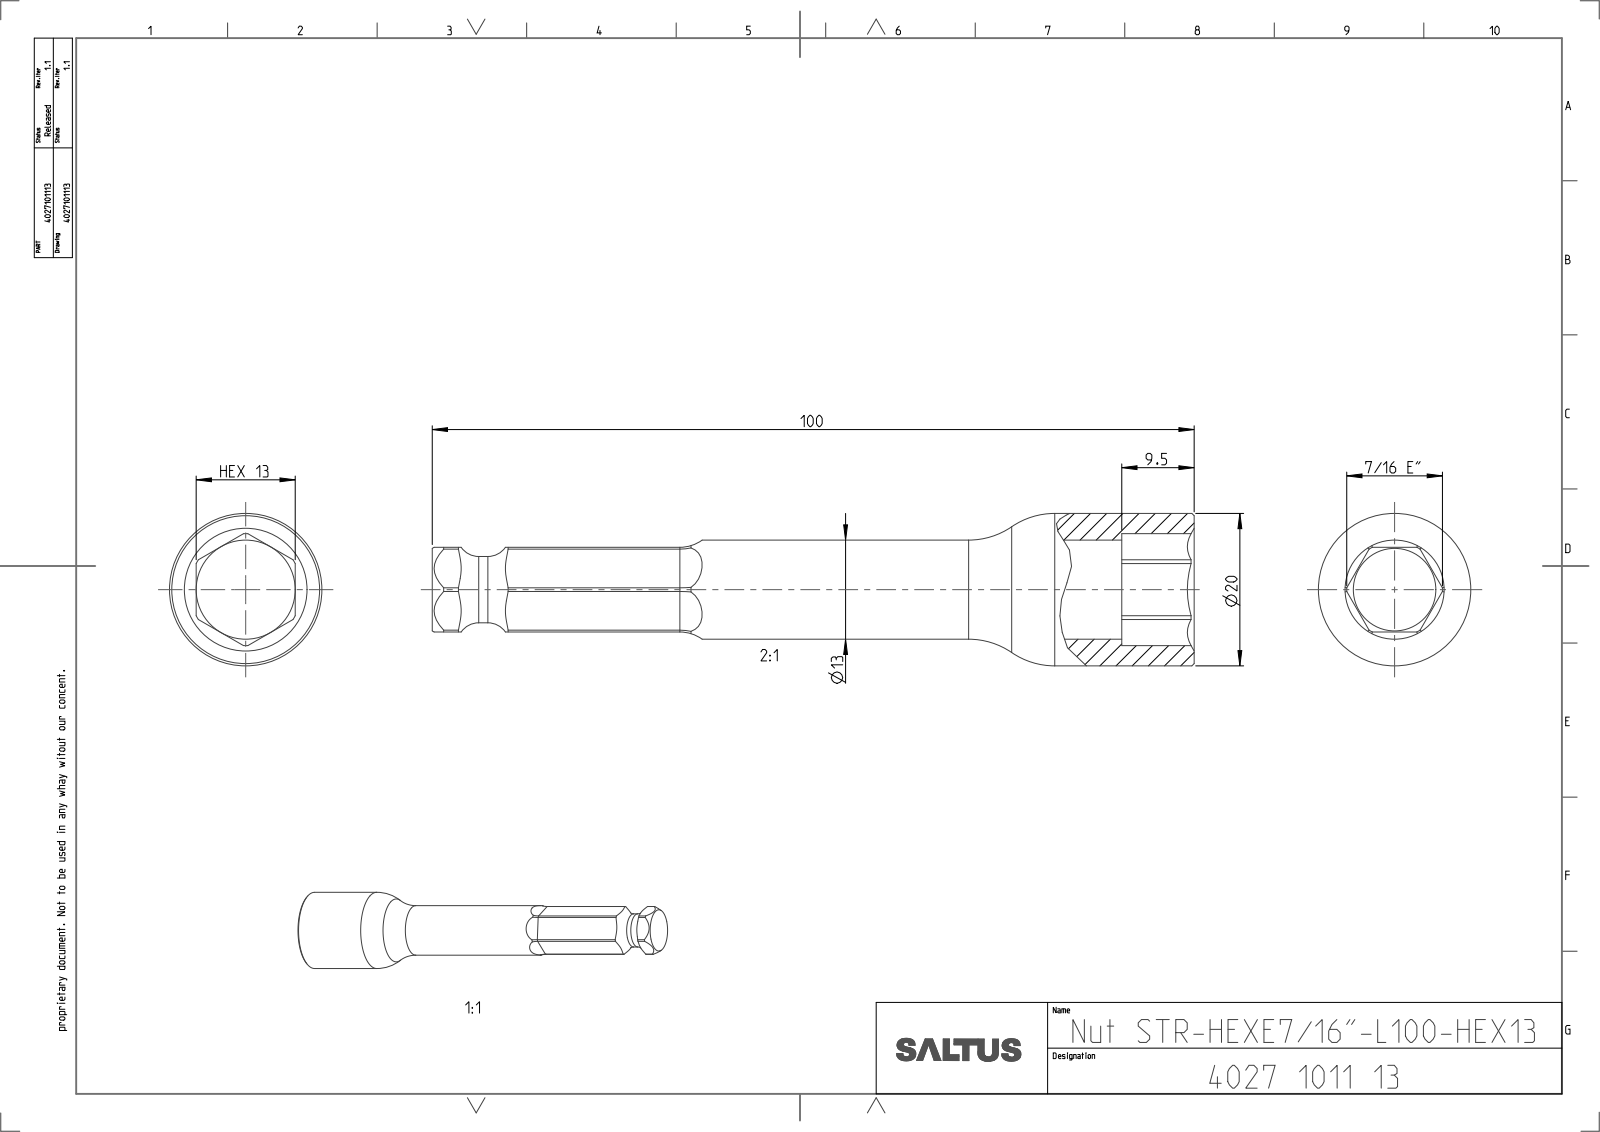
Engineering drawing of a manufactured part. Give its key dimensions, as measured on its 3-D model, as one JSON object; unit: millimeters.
{"part_name": "4027101113", "step_written_by": "CREO PARAMETRIC BY PTC INC, 2022414 (CONFIG_CONTROL_DESIGN)", "units": "millimeters", "bodies": {"solids": 1, "faces": 80, "planar": 26, "cylindrical": 32, "other": 22}, "overall_size": [100, 20, 20], "volume_mm3": 13596, "surface_area_mm2": 5748, "round_holes": [[13, 1]], "round_bosses_or_shafts": [[20, 1], [8.7, 1]], "partial_cylinders_radius": [[5, 6], [6.28, 1], [7.34, 1]], "face_to_face_distances": [11.1, 13, 100, 90.5, 9.5]}
